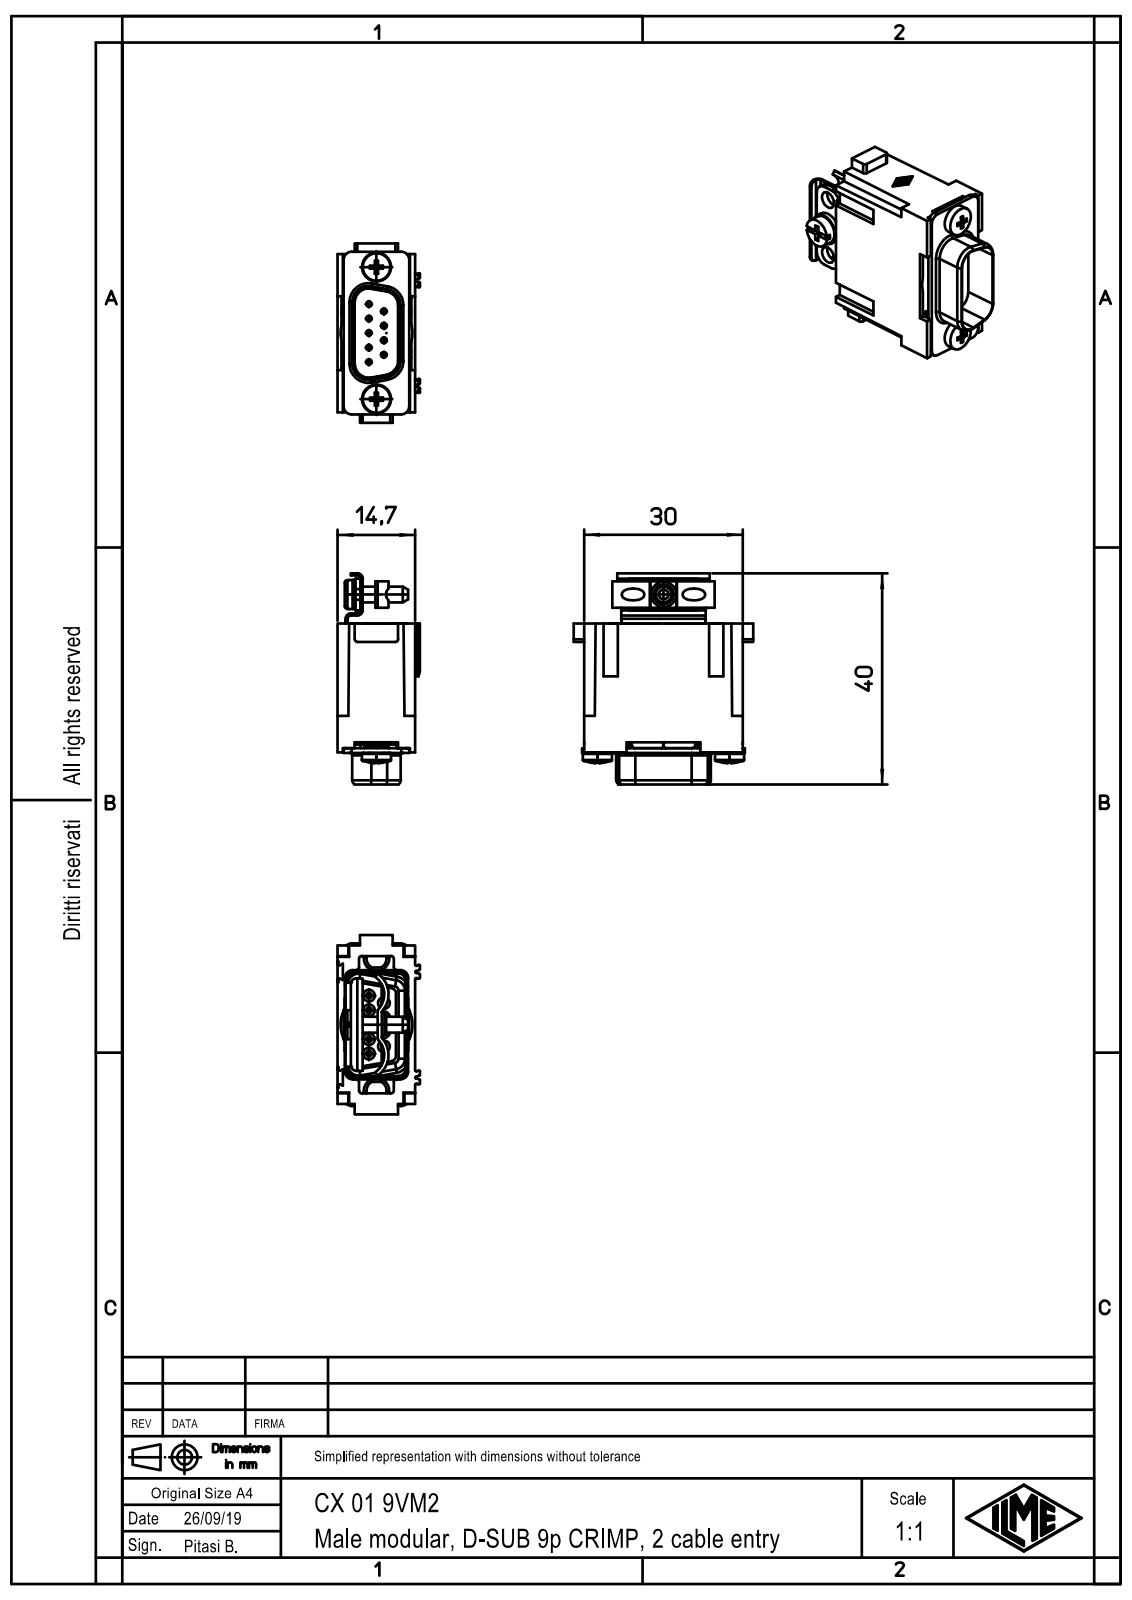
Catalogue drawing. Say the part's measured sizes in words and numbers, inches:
The part is named "CX 01 9VM2". Its 3-D file was written by "Creo Elements/Direct Modeling 20.1B 02-Apr-2019 (C) Parametric Technology GmbH (AUTOMOTIVE_DESIGN)". It is 1 solid with 249 faces: 163 planar, 78 cylindrical and 8 other. Overall it measures 1.575 by 1.339 by 0.614 inches. Its volume is 0.678 cubic inches and its surface area 7.725 square inches. Round holes: 9 of diameter 0.043, 1 of diameter 0.126. Round bosses or shafts: 3 of diameter 0.217, 1 of diameter 0.236, 1 of diameter 0.15, 1 of diameter 0.118, 1 of diameter 0.102. Partial cylindrical surfaces (rounded edges, fillets, slot ends): 11 of radius 0.039, 4 of radius 0.02, 4 of radius 0.059, 4 of radius 0.079, 4 of radius 0.102, 4 of radius 0.122, 3 of radius 0.024, 2 of radius 0.008. The main face-to-face distances are 0.579, 0.02, 1.181, 0.079, 0.965, 0.039, 0.128, 0.081, 0.059, 0.451. The hole center spacings are 0.124, 0.197, 0.108, 0.292, 0.216, 0.108, 0.124, 0.216.
